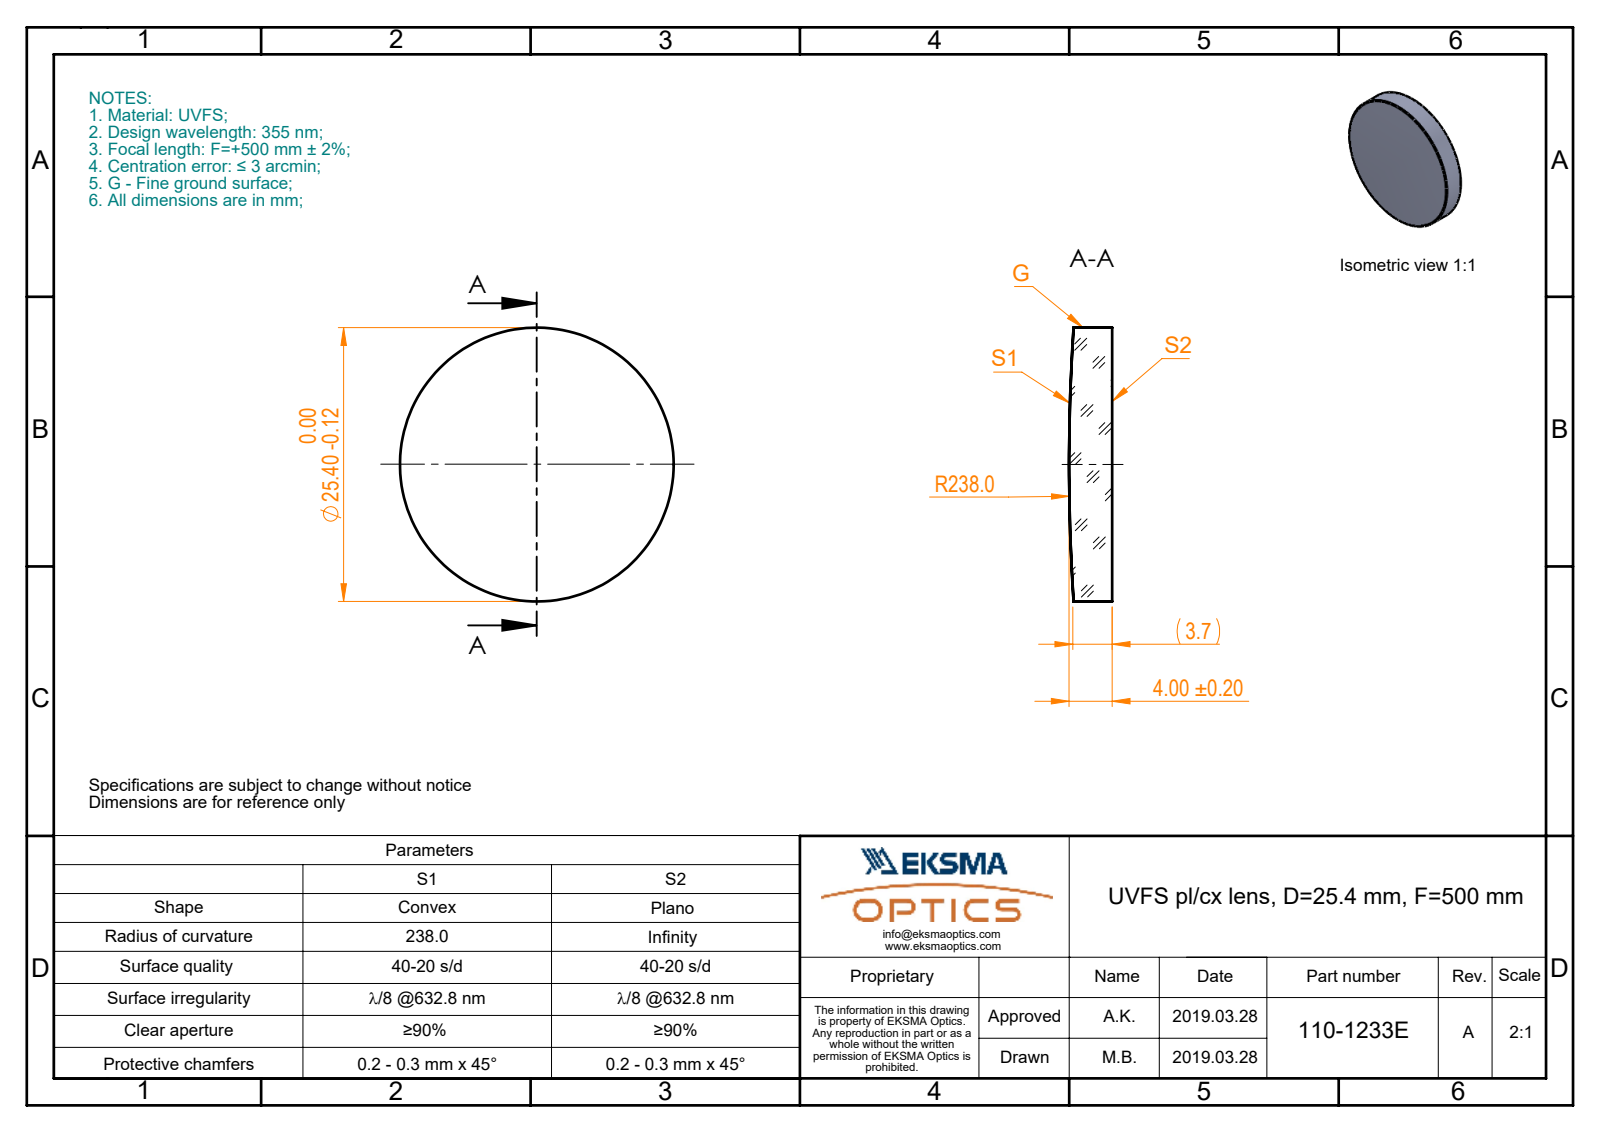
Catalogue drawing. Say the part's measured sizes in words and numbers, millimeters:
The part is named "110-1233E UVFS pl-cx 25.4 F500". Its 3-D file was written by "SolidWorks 2017 (CONFIG_CONTROL_DESIGN)". It is 1 solid with 5 faces: 1 planar, 2 cylindrical and 2 other. Overall it measures 25.4 by 25.4 by 4 millimeters. Its volume is 1 941 cubic millimeters and its surface area 1 306 square millimeters. Round bosses or shafts: 1 of diameter 25.4.
